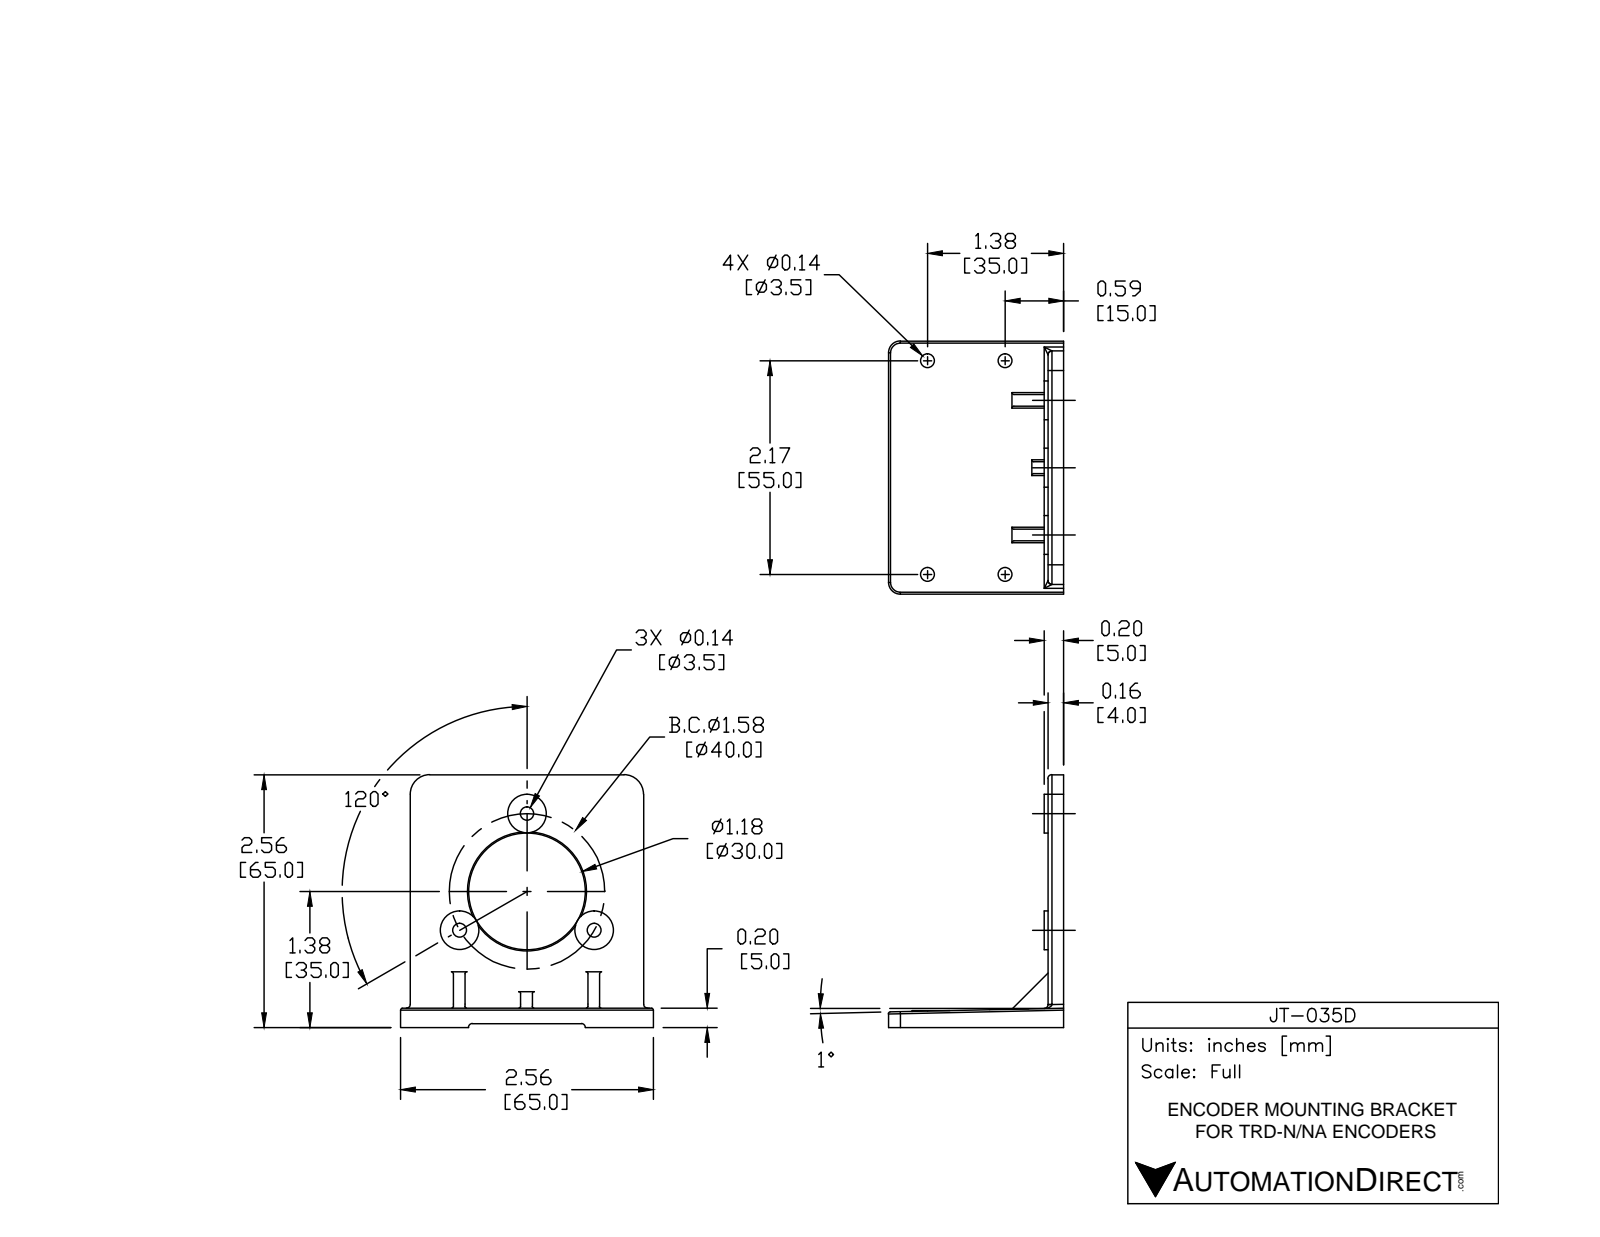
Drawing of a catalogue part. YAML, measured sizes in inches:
part_name: "JT-035Db2"
step_written_by: "SolidWorks 2017 (AUTOMOTIVE_DESIGN)"
units: inches
bodies: {solids: 1, faces: 368, planar: 99, cylindrical: 166, other: 103}
overall_size: [2.559, 2.559, 1.772]
volume: 1.291
surface_area: 22.33
round_holes:
  - {diameter: 0.138, count: 7}
  - {diameter: 1.181, count: 1}
round_bosses_or_shafts:
  - {diameter: 0.394, count: 3}
partial_cylinders:
  - {radius: 0.039, count: 62}
  - {radius: 0.02, count: 41}
  - {radius: 0.197, count: 6}
  - {radius: 0.118, count: 2}
  - {radius: 0.709, count: 1}
face_to_face_distances: [0.039, 0.118, 0.157, 0.02, 0.059, 0.098, 2.461, 2.559, 1.772, 0.197]
hole_center_spacings: [0.787, 1.364, 2.165, 2.304]
